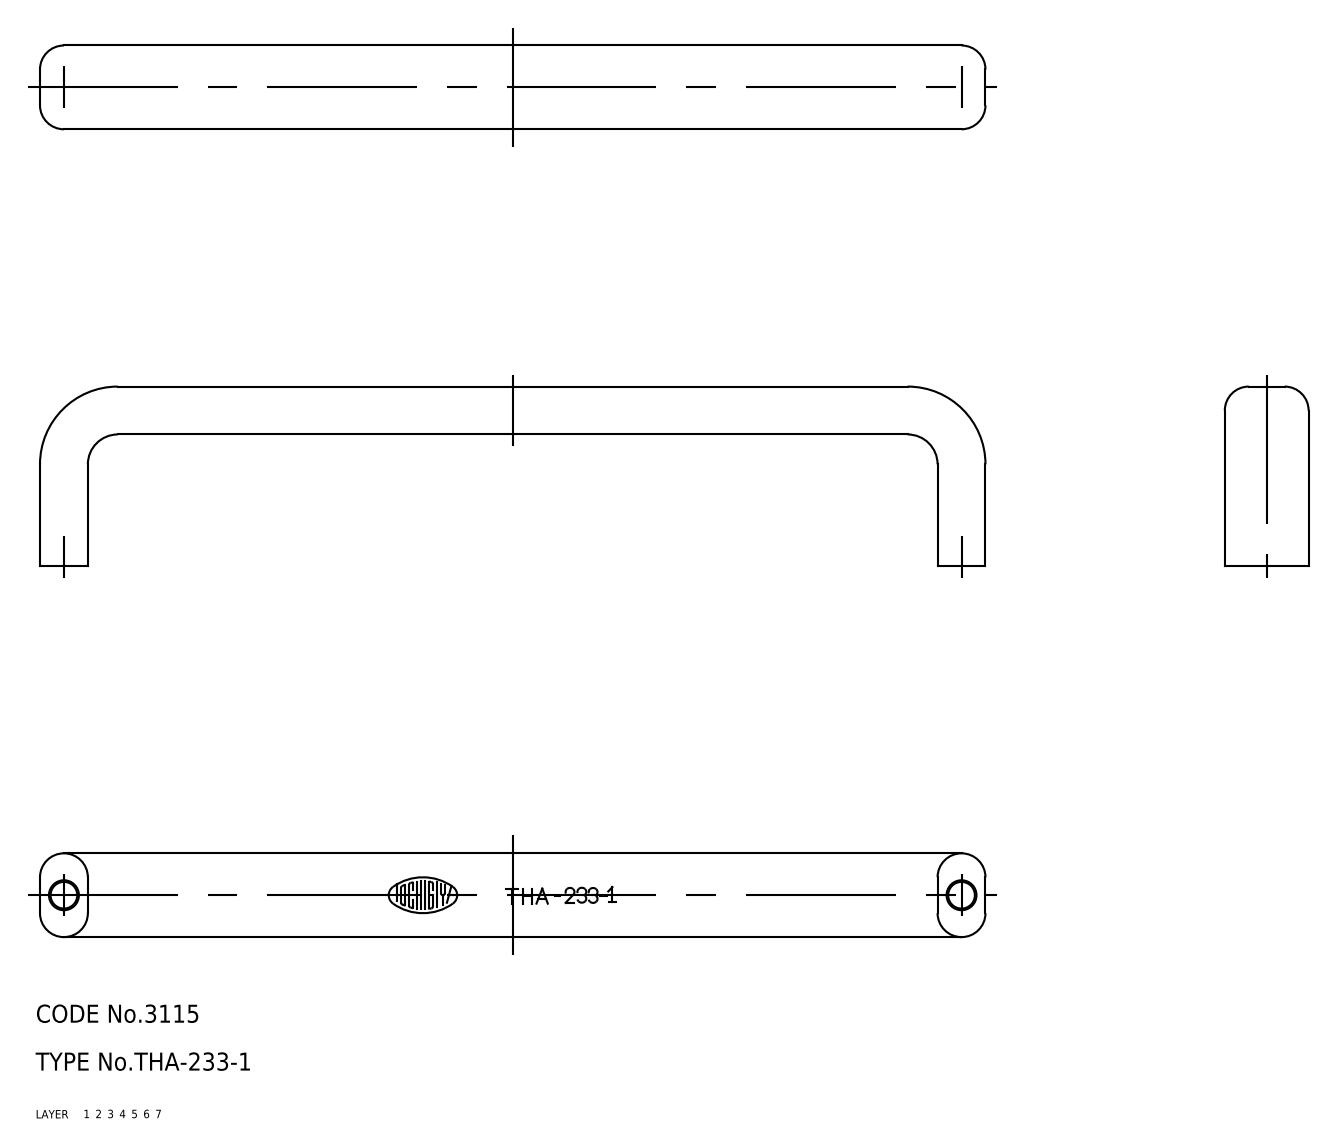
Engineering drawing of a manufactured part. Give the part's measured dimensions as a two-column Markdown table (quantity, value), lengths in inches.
| quantity | value |
| --- | --- |
| part name | pull |
| STEP written by | CADfix (AUTOMOTIVE_DESIGN) |
| units | inches |
| bodies | 1 solid, 28 faces (0 planar, 0 cylindrical, 28 other) |
| overall size | 6.22 × 1.181 × 0.551 |
| volume | 1.141 in³ |
| surface area | 11.97 in² |
